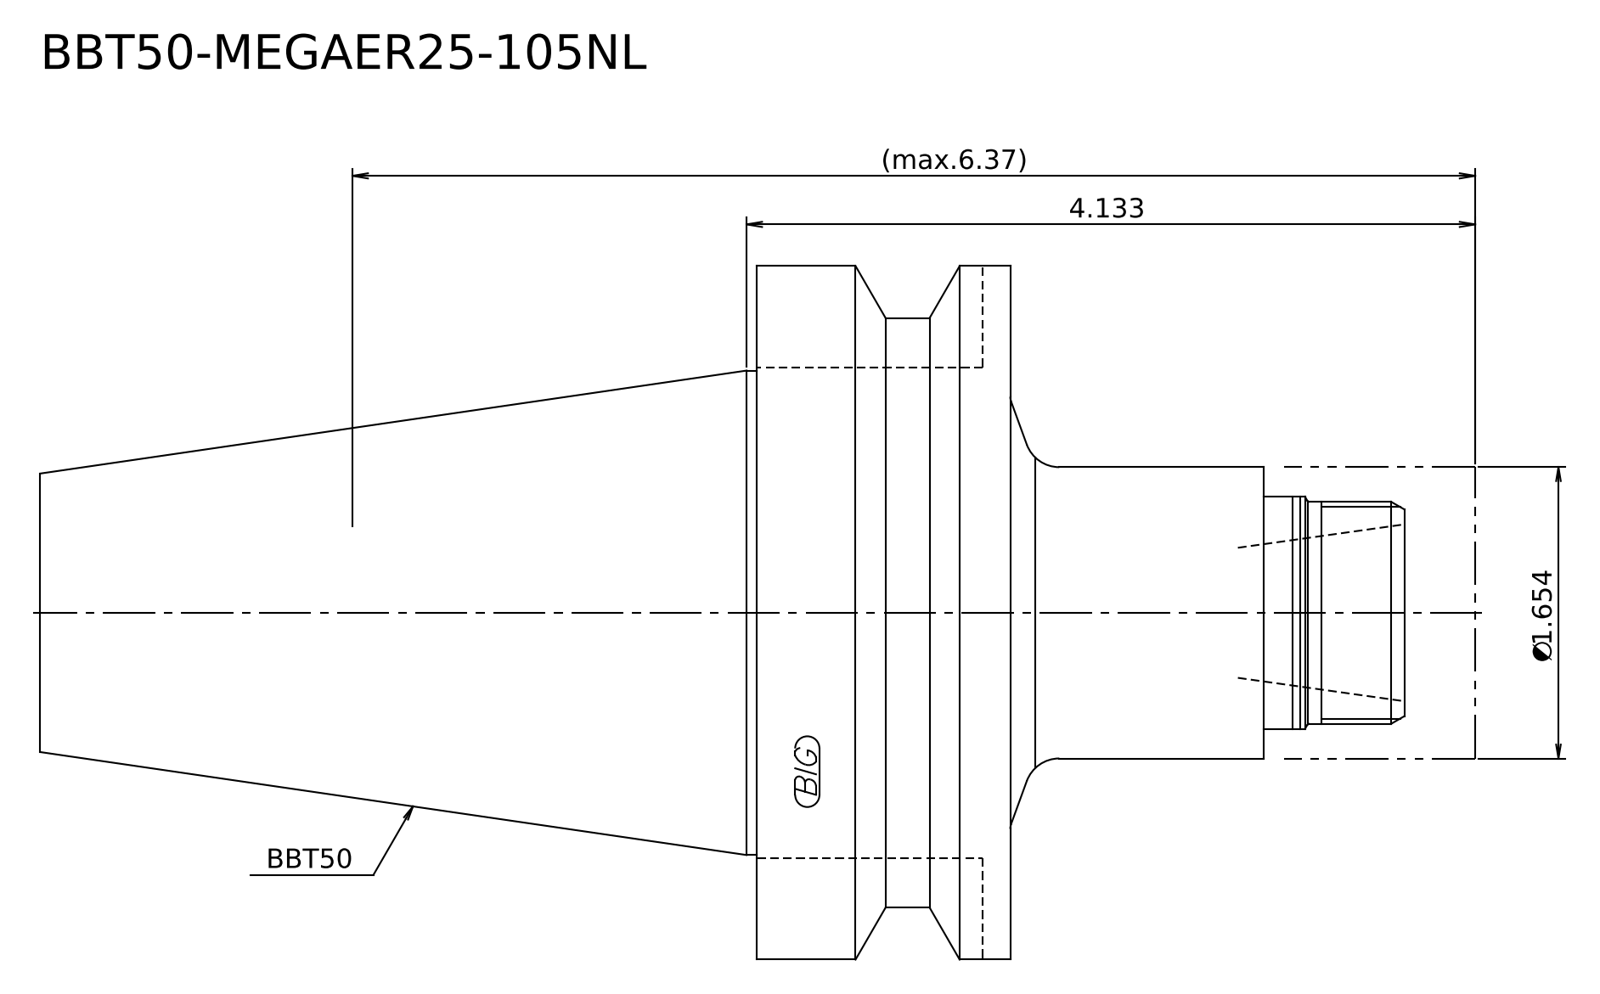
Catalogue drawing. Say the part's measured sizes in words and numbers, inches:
Its 3-D file was written by "Kubotek KeyCreator 2011 V10.0.2 (22737) (automotive_design)". It is 2 solids with 21 faces: 7 planar, 8 cylindrical and 6 other. Overall it measures 8.142 by 3.937 by 3.937 inches. Its volume is 38.29 cubic inches and its surface area 88.86 square inches. Round bosses or shafts: 1 of diameter 3.937, 1 of diameter 3.346, 1 of diameter 2.75, 1 of diameter 1.654, 1 of diameter 1.319, 1 of diameter 1.26. The main face-to-face distances are 1.437, 1.555, 2.992, 1.083, 2.638, 4.075, 8.142, 7.059, 5.504, 4.067.
